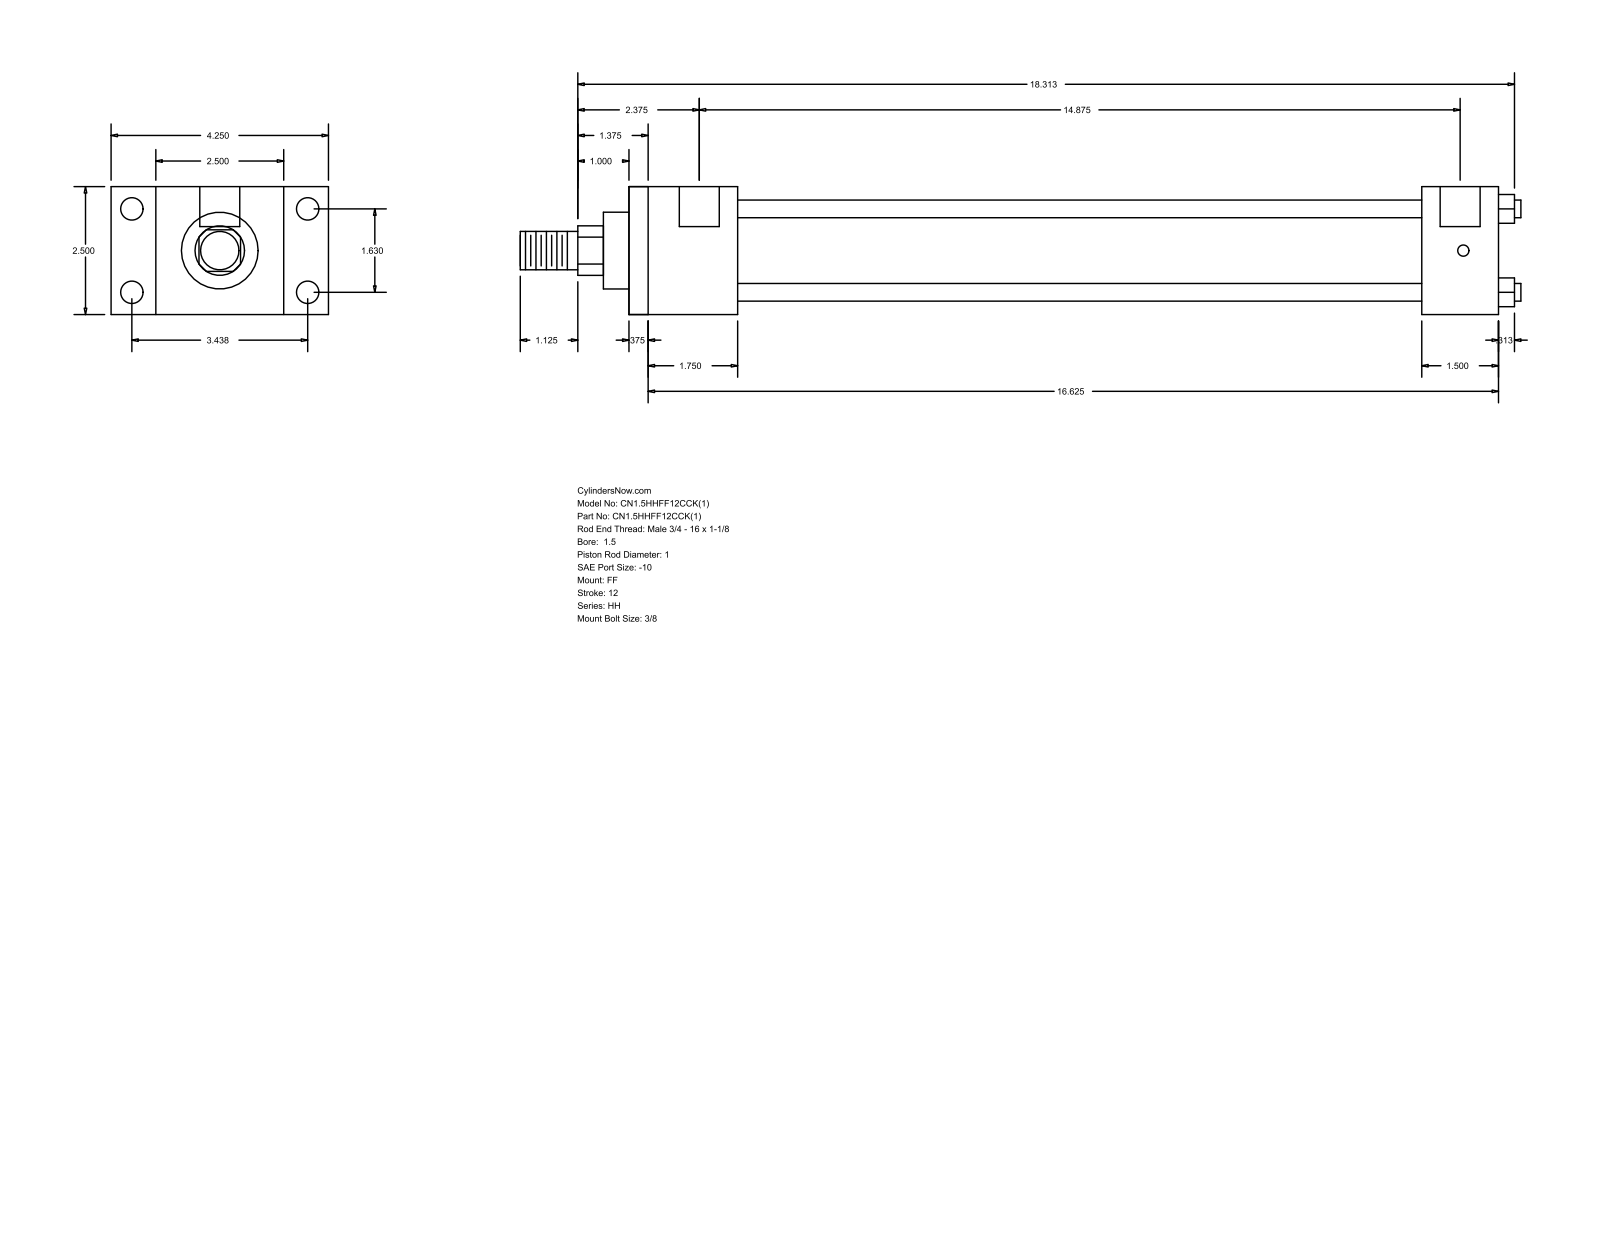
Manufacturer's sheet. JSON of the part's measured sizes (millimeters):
{"part_name": "HH_FF__0150_1", "step_written_by": "GSSL Pune (CONFIG_CONTROL_DESIGN)", "units": "millimeters", "bodies": {"solids": 0, "faces": 92, "planar": 64, "cylindrical": 28, "other": 0}, "overall_size": [496.89, 107.95, 63.5], "round_holes": [[5.56, 4], [11.13, 4], [19.84, 2]], "round_bosses_or_shafts": [[8.76, 4], [44.45, 1], [38.1, 1], [25.4, 1], [19.05, 1]], "partial_cylinders_radius": [[12.29, 1]], "face_to_face_distances": [63.5, 431.8, 9.52, 422.28, 38.1, 53.98, 44.46, 377.82, 393.7, 384.18], "hole_center_spacings": [1.59, 41.4, 87.32, 96.64, 379.41, 381, 377.82]}
